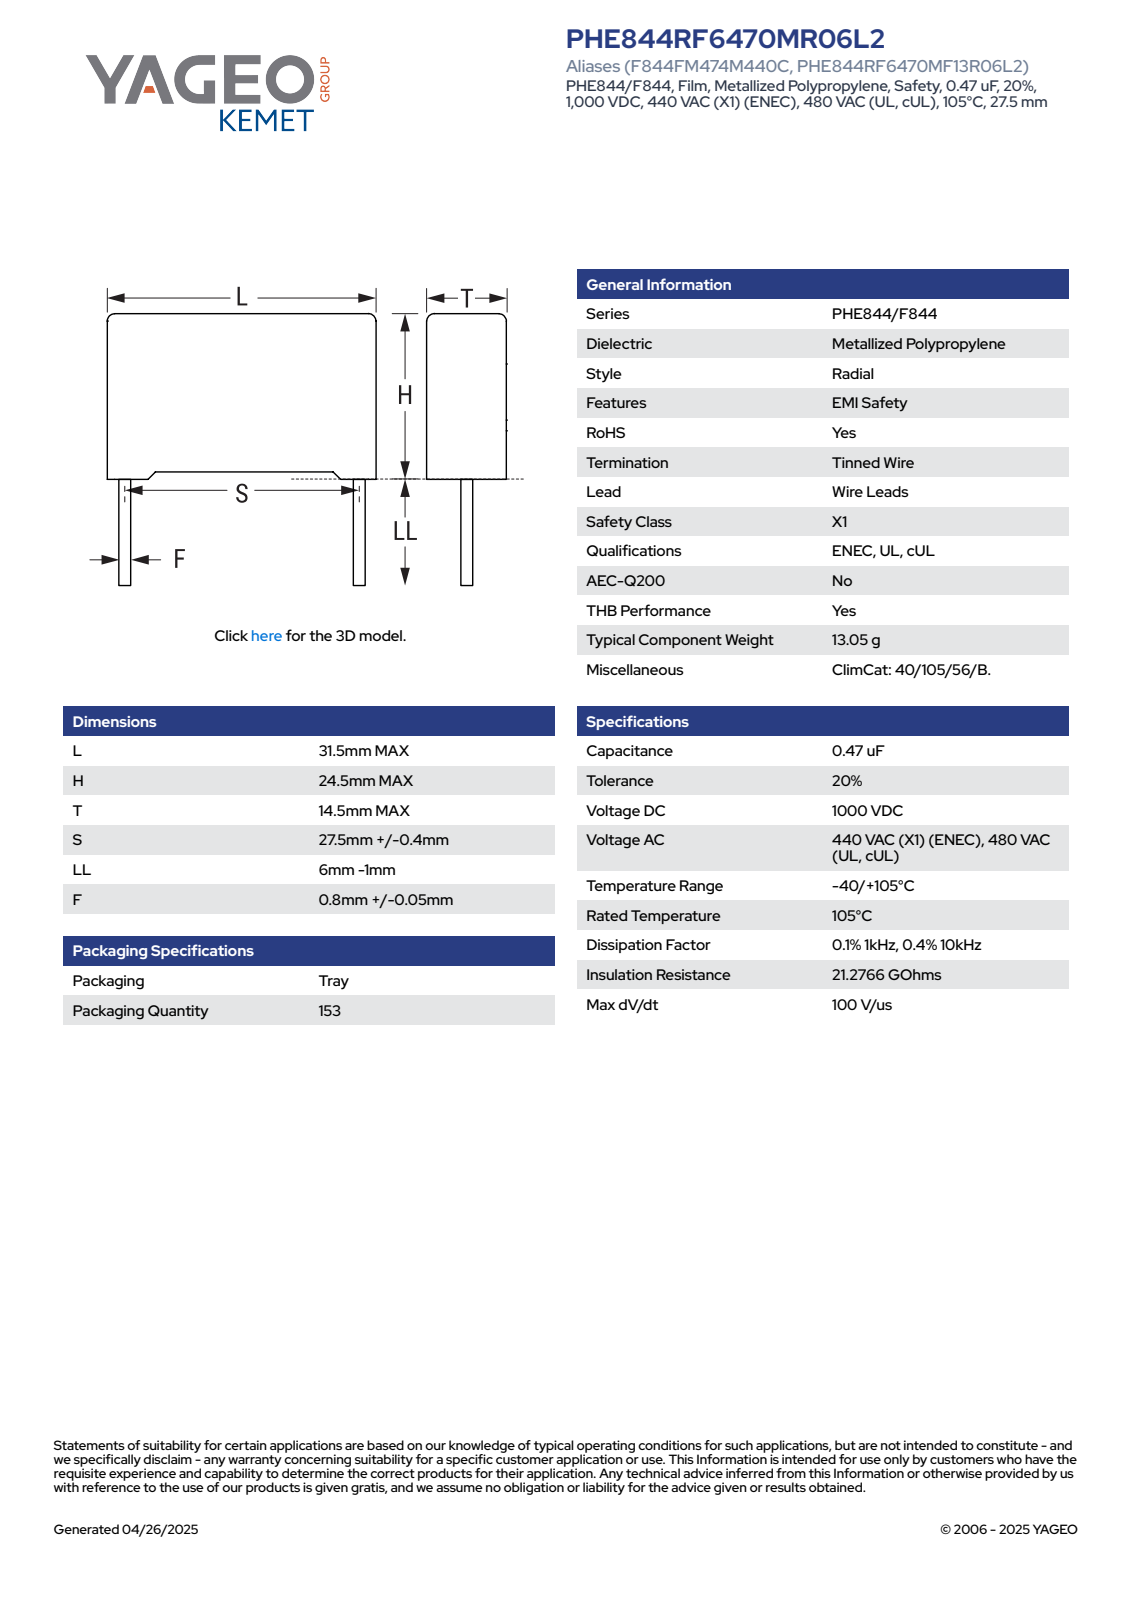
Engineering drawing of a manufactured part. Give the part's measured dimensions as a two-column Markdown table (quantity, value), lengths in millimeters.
| quantity | value |
| --- | --- |
| part name | CFR_RB2_31.5X24.5X14.5_L31.5H24.5T14.5S27.5LL5F0.85 |
| STEP written by | SolidWorks 2021 (AUTOMOTIVE_DESIGN) |
| units | millimeters |
| bodies | 4 solids, 85 faces (77 planar, 8 cylindrical, 0 other) |
| overall size | 31.5 × 29.5 × 14.51 |
| volume | 10 850 mm³ |
| surface area | 3 242 mm² |
| round bosses / shafts (diameter × count) | 0.85 × 2 |
| partial cylindrical surfaces (radius × count) | 0.5 × 4 |
| main face-to-face distances | 14.5, 31.5, 23.66, 23.75, 0.75, 0.84, 24.5, 1.05, 30.45, 14.51 |
